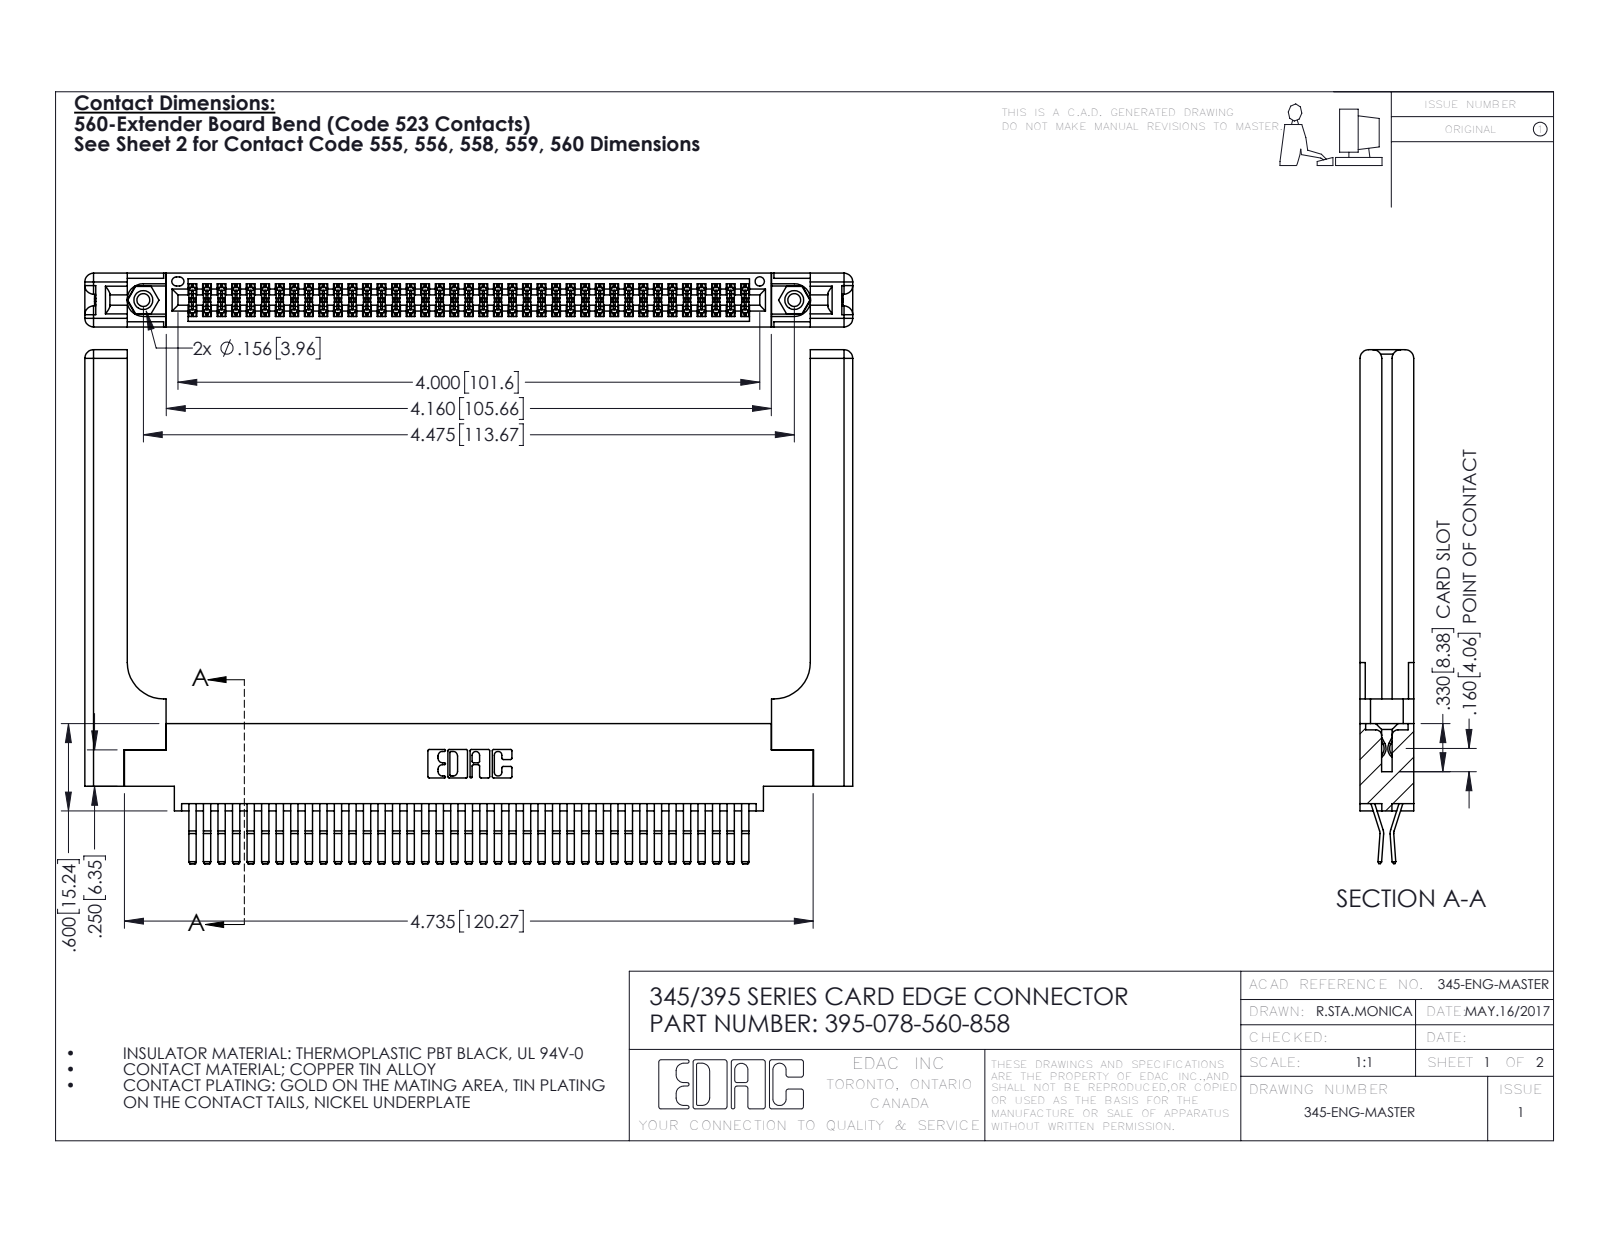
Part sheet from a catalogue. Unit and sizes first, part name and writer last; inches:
Units: inches
Overall size (bounding box): 5.279 × 3.532 × 0.37
Round holes (diameter × count): ⌀0.089 ×2, ⌀0.125 ×2, ⌀0.156 ×2, ⌀0.064 ×1
Round bosses / shafts (diameter × count): ⌀0.155 ×2
Partial cylindrical surfaces — rounded edges, fillets, slot ends (radius × count): R0.006 ×117, R0.01 ×22, R0.06 ×16, R0.007 ×6, R0.031 ×6, R0.026 ×3, R0.01 ×2, R0.014 ×2
Main face-to-face distances: 0.37, 0.072, 0.298, 0.025, 0.098, 0.272, 0.2, 0.225, 0.148, 0.15
Hole centre spacings: 0.27, 4.239, 4.475
Volume: 1.335 in³ · Surface area: 40.7 in²
Bodies: 83 solids, 4442 faces (2806 planar, 1576 cylindrical, 60 other)
Part name (STEP PRODUCT): 345-220-058_345-220-058; 395-078-560-858; 345-250-001_345-250-001-102; 345-292-001_560 Tail (+1 more)
STEP written by: SolidWorks 2016 (CONFIG_CONTROL_DESIGN)
